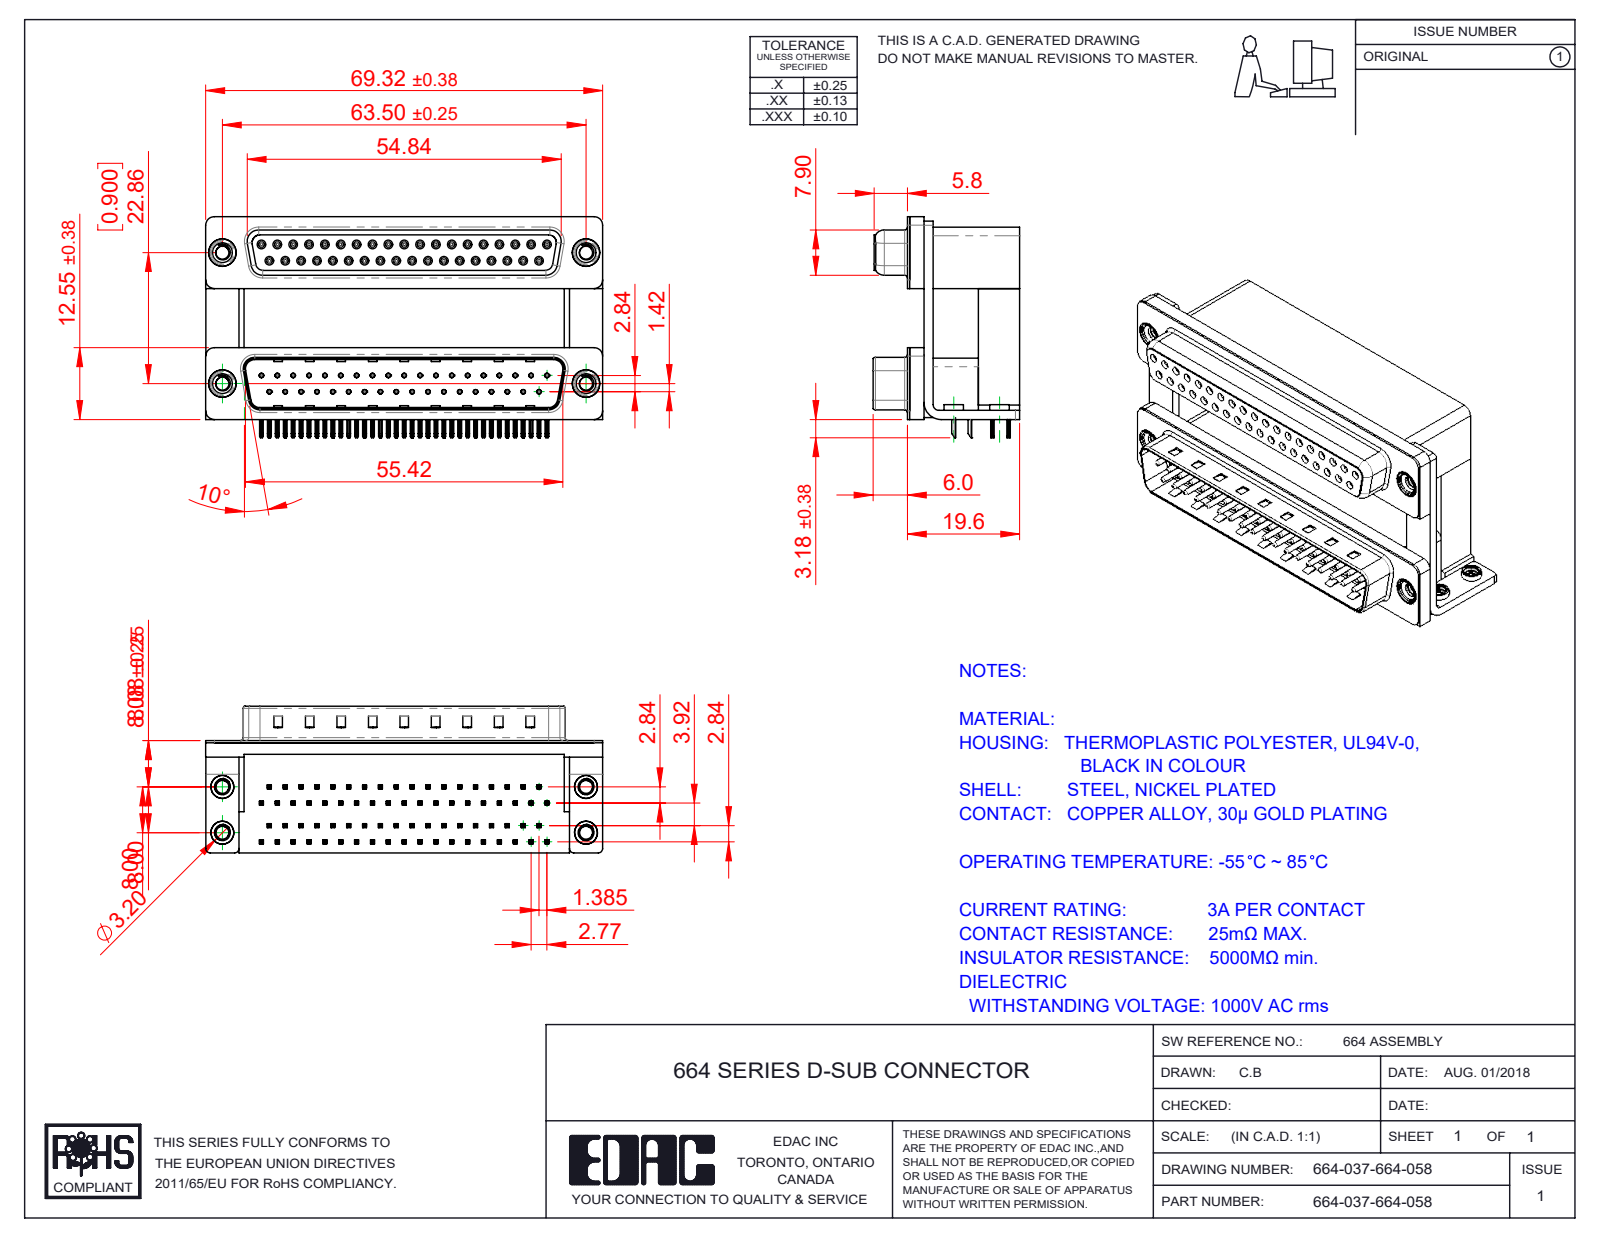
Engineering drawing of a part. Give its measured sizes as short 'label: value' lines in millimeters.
name: 664 Shell Plug_37 Contacts; 664 Mounting Bracket_ThruH; 664 Shell Receptacle_37 Contacts; 664 Housing Upper_37 Contacts H (+8 more)
written by: SolidWorks 2020 (CONFIG_CONTROL_DESIGN)
unit: mm
bodies: 89 solids, 9085 faces (4753 planar, 2253 cylindrical, 2079 other)
size: 69.32 × 38.59 × 25.6
volume: 32 719 mm³; area: 34 339 mm²
holes: 74× ⌀0.8, 37× ⌀0.35, 37× ⌀0.9, 8× ⌀2.26, 4× ⌀2.75, 4× ⌀3.2, 4× ⌀3.5, 4× ⌀4, 4× ⌀4.8, 4× ⌀5
bosses: 37× ⌀1.2, 37× ⌀0.75, 4× ⌀4.9, 4× ⌀4.75, 4× ⌀4, 4× ⌀3.9, 4× ⌀3.4
rounds: 296× R0.1, 148× R0.15, 148× R0.25, 74× R0.12, 74× R0.35, 37× R0.34, 18× R0.28, 13× R1.5
face distances: 19.2, 0.4, 12, 7.2, 2.19, 2.84, 0.65, 22.5, 10.69, 22.86
hole spacings: 2.77, 5.54, 3.16, 8.31, 11.08, 13.85, 16.62, 19.39
